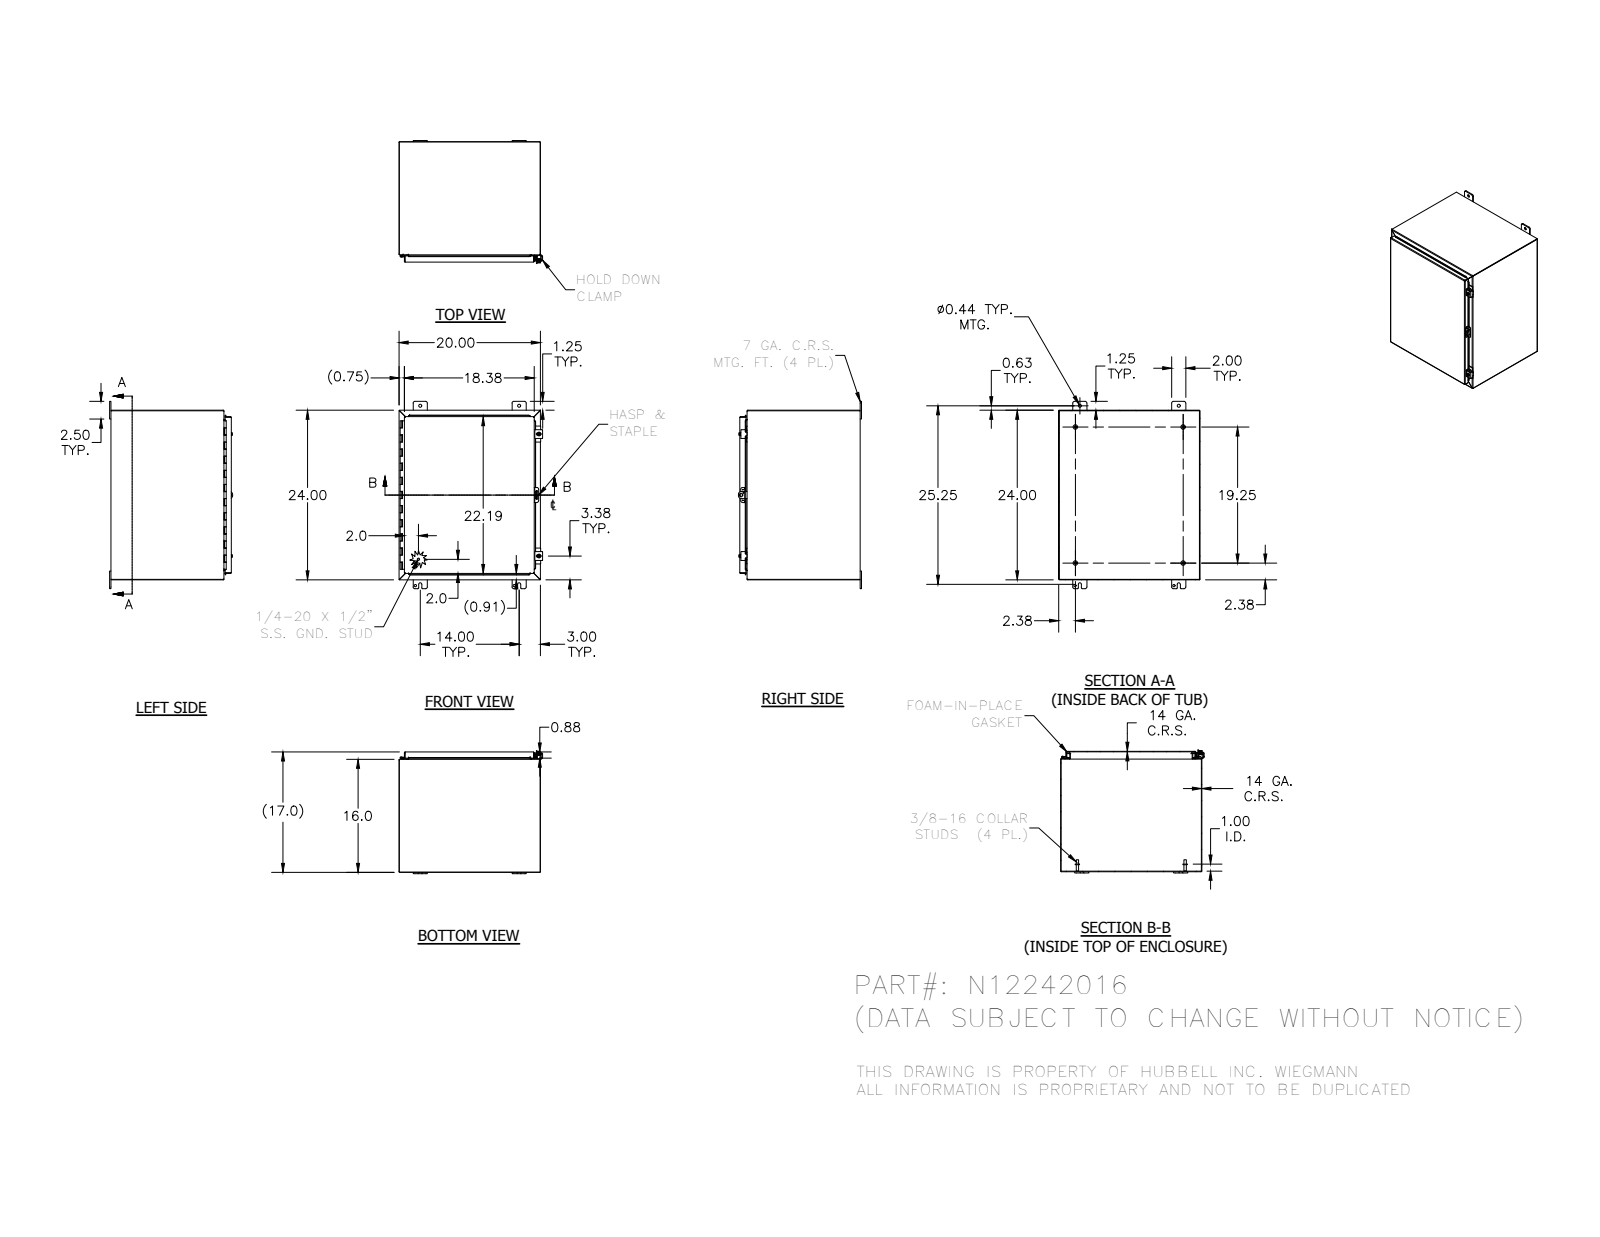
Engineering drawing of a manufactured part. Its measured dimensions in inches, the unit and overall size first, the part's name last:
Units: inches
Overall size (bounding box): 26.5 × 20.311 × 17.41
Round holes (diameter × count): ⌀0.313 ×4, ⌀0.438 ×4, ⌀0.11 ×3, ⌀0.211 ×2, ⌀0.281 ×2, ⌀0.3 ×2, ⌀0.125 ×1, ⌀0.156 ×1, ⌀0.5 ×1
Round bosses / shafts (diameter × count): ⌀0.625 ×4, ⌀0.33 ×4, ⌀0.25 ×4, ⌀0.52 ×2, ⌀0.5 ×2, ⌀0.35 ×2, ⌀0.115 ×2, ⌀0.337 ×1
Partial cylindrical surfaces — rounded edges, fillets, slot ends (radius × count): R0.03 ×27, R0.125 ×25, R0.25 ×25, R0.031 ×21, R0.105 ×21, R0.063 ×13, R0.1 ×4, R0.141 ×4
Main face-to-face distances: 0.074, 16.959, 19.926, 23.926, 16.885, 17.033, 20, 19.852, 23.852, 24
Hole centre spacings: 1.593, 14, 24, 27.785, 0.791, 13.39, 14.757, 22.574
Volume: 204.1 in³ · Surface area: 5 384 in²
Bodies: 29 solids, 870 faces (507 planar, 262 cylindrical, 101 other)
Part name (STEP PRODUCT): N12242016; 34840; 38413; N122016TB (+8 more)
STEP written by: Autodesk Inventor 2012 (AUTOMOTIVE_DESIGN)
